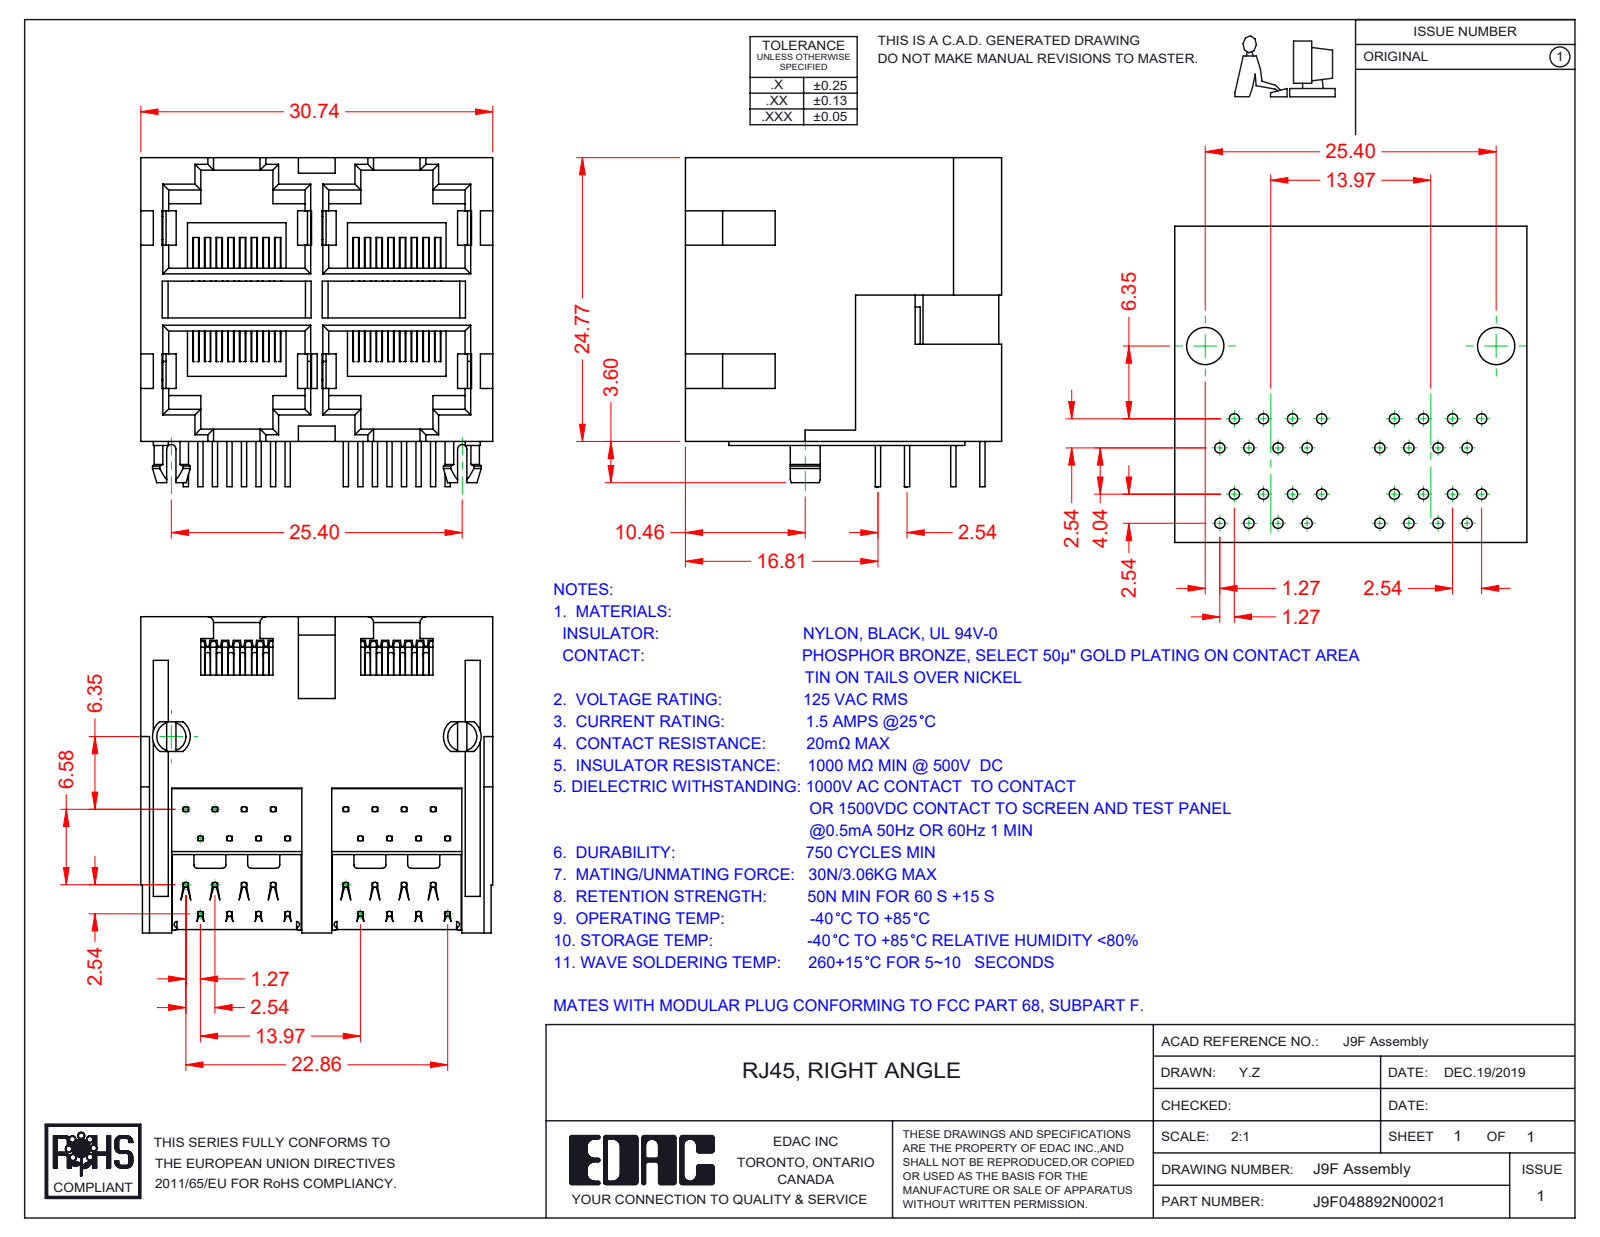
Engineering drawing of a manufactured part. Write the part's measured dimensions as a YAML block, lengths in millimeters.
part_name: "9F Contact Lock Upper; 9F Contacts Upper; 9F Contacts Lower; RJ9F048892N00021 (+2 more)"
step_written_by: "SolidWorks 2016 (CONFIG_CONTROL_DESIGN)"
units: millimeters
bodies: {solids: 37, faces: 2810, planar: 1899, cylindrical: 557, other: 354}
overall_size: [30.74, 28.71, 27.6]
volume: 11763
surface_area: 19774
round_bosses_or_shafts:
  - {diameter: 0.46, count: 144}
partial_cylinders:
  - {radius: 0.2, count: 63}
  - {radius: 0.5, count: 25}
  - {radius: 0.3, count: 9}
  - {radius: 0.25, count: 4}
  - {radius: 0.4, count: 2}
  - {radius: 0.45, count: 2}
  - {radius: 1.5, count: 2}
  - {radius: 1.65, count: 2}
face_to_face_distances: [13.97, 1, 0.35, 12.7, 15, 13.05, 11.98, 1.05, 13.62, 5.5]
